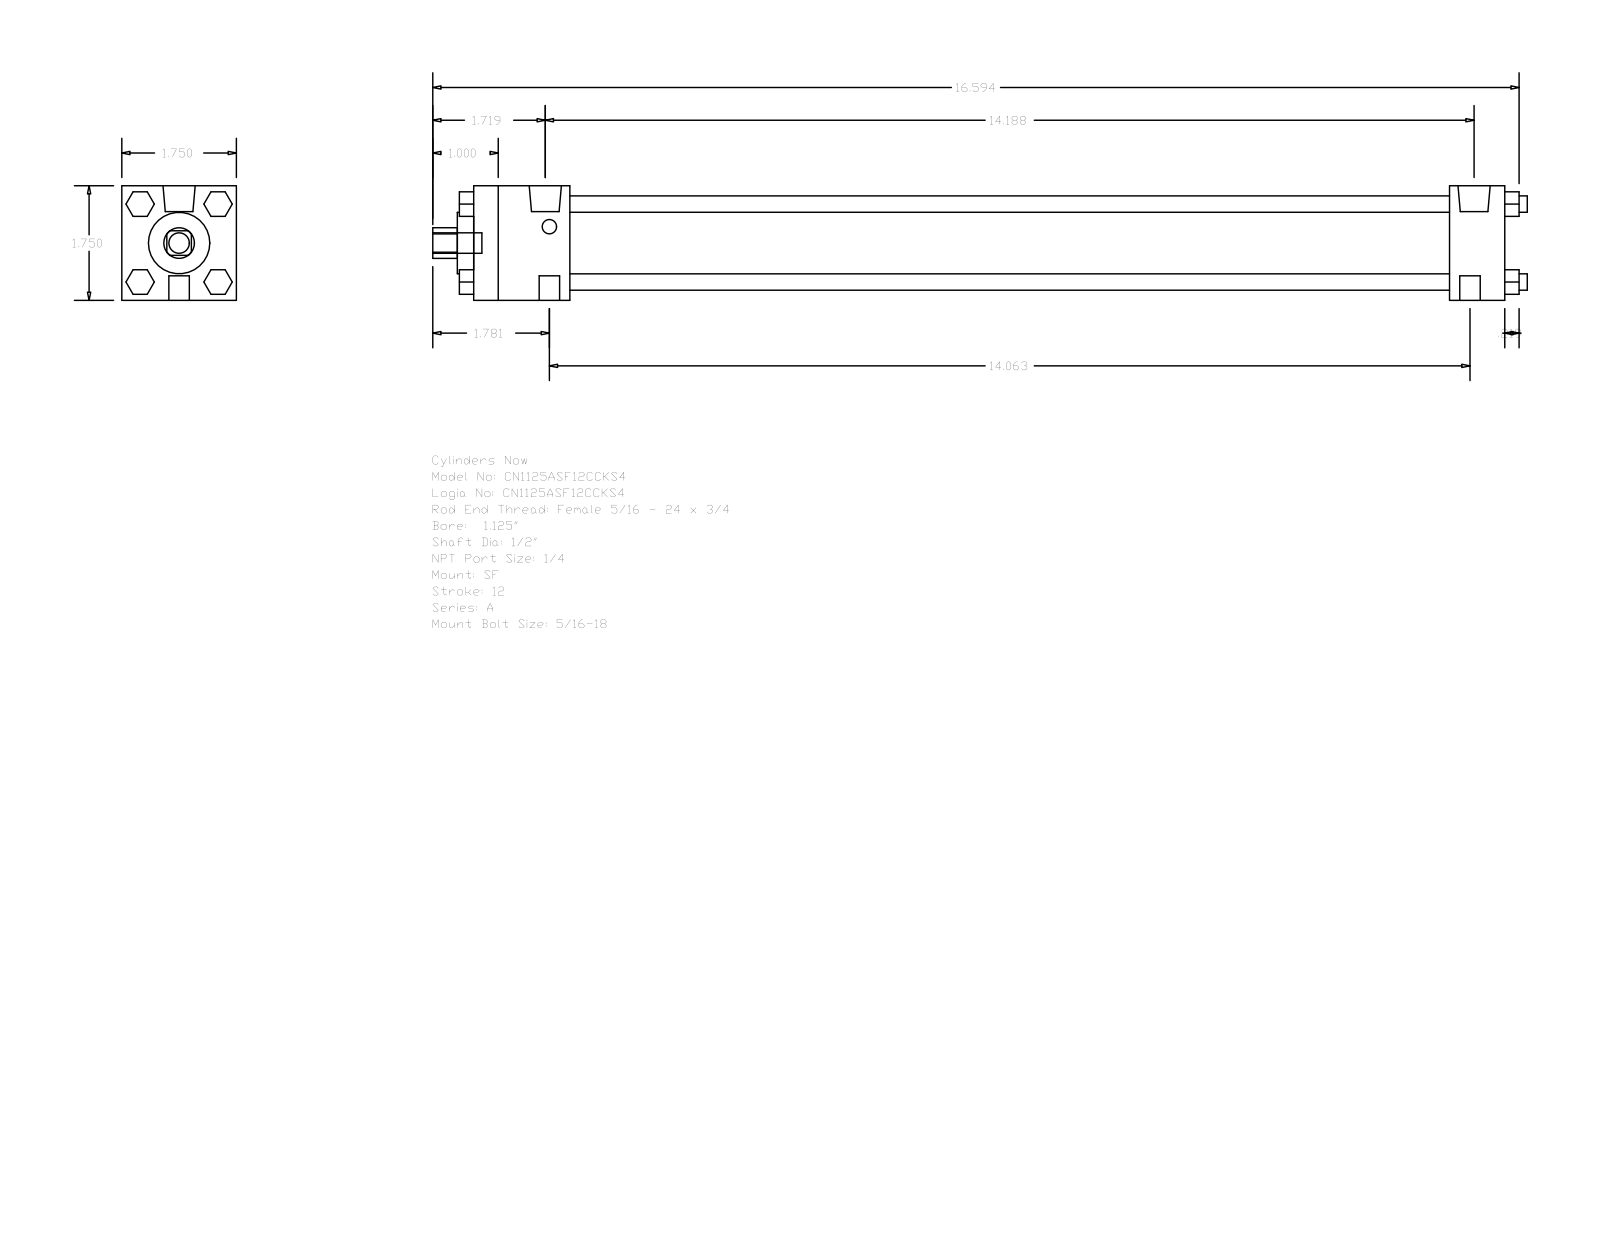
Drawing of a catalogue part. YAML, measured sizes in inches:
part_name: "A_SF__0112_0.5"
step_written_by: "GSSL Pune (CONFIG_CONTROL_DESIGN)"
units: inches
bodies: {solids: 0, faces: 120, planar: 92, cylindrical: 28, other: 0}
overall_size: [16.719, 1.75, 1.75]
round_holes:
  - {diameter: 0.5, count: 1}
  - {diameter: 0.937, count: 1}
  - {diameter: 1.255, count: 1}
round_bosses_or_shafts:
  - {diameter: 0.25, count: 4}
  - {diameter: 0.313, count: 3}
  - {diameter: 0.492, count: 2}
  - {diameter: 0.219, count: 2}
partial_cylinders:
  - {radius: 0.234, count: 1}
face_to_face_distances: [1.75, 15.75, 14.906, 0.844, 1.469, 13.437, 14.281, 0.375, 0.22, 0.375]
